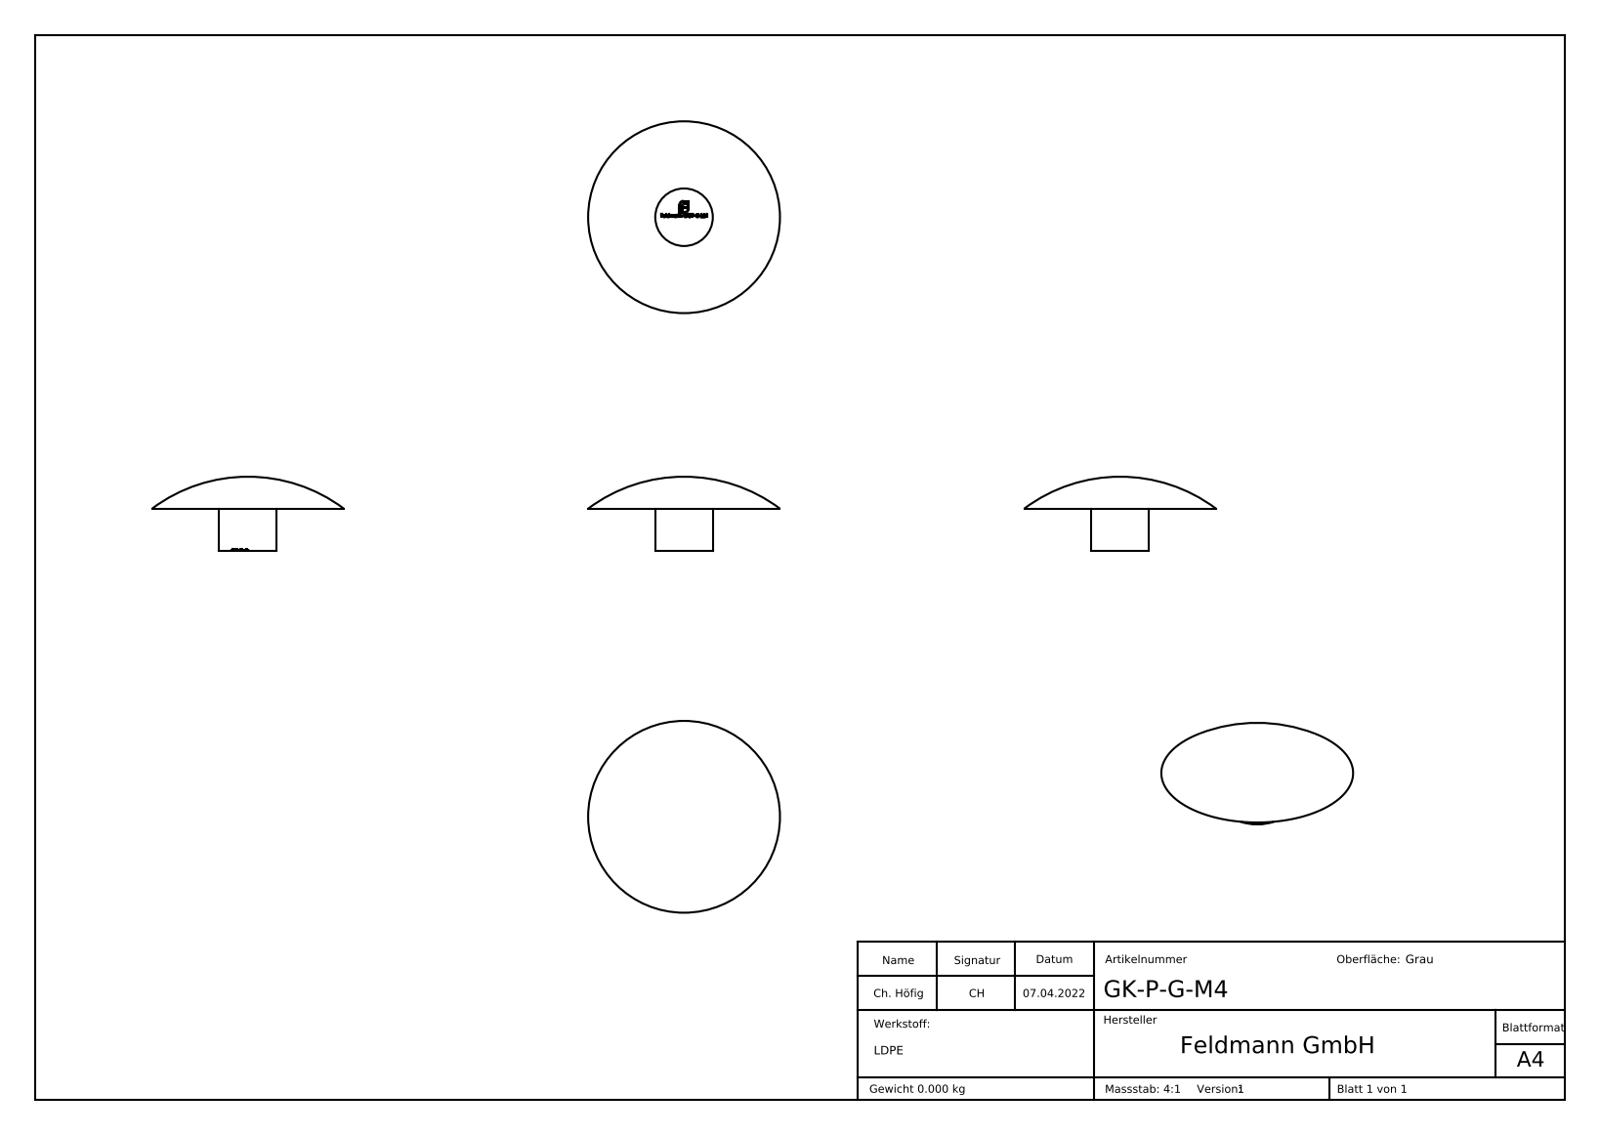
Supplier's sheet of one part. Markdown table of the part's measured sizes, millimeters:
| quantity | value |
| --- | --- |
| part name | GK-P-G-M4 |
| STEP written by | SolidWorks 2018 (CONFIG_CONTROL_DESIGN) |
| units | millimeters |
| bodies | 1 solid, 260 faces (166 planar, 1 cylindrical, 93 other) |
| overall size | 9 × 9 × 3.5 |
| volume | 61 mm³ |
| surface area | 153 mm² |
| round bosses / shafts (diameter × count) | 2.7 × 1 |
| main face-to-face distances | 2, 1.9, 0.4, 0.34, 0.57, 0.7, 0.6, 0.49, 0.62, 0.77 |
